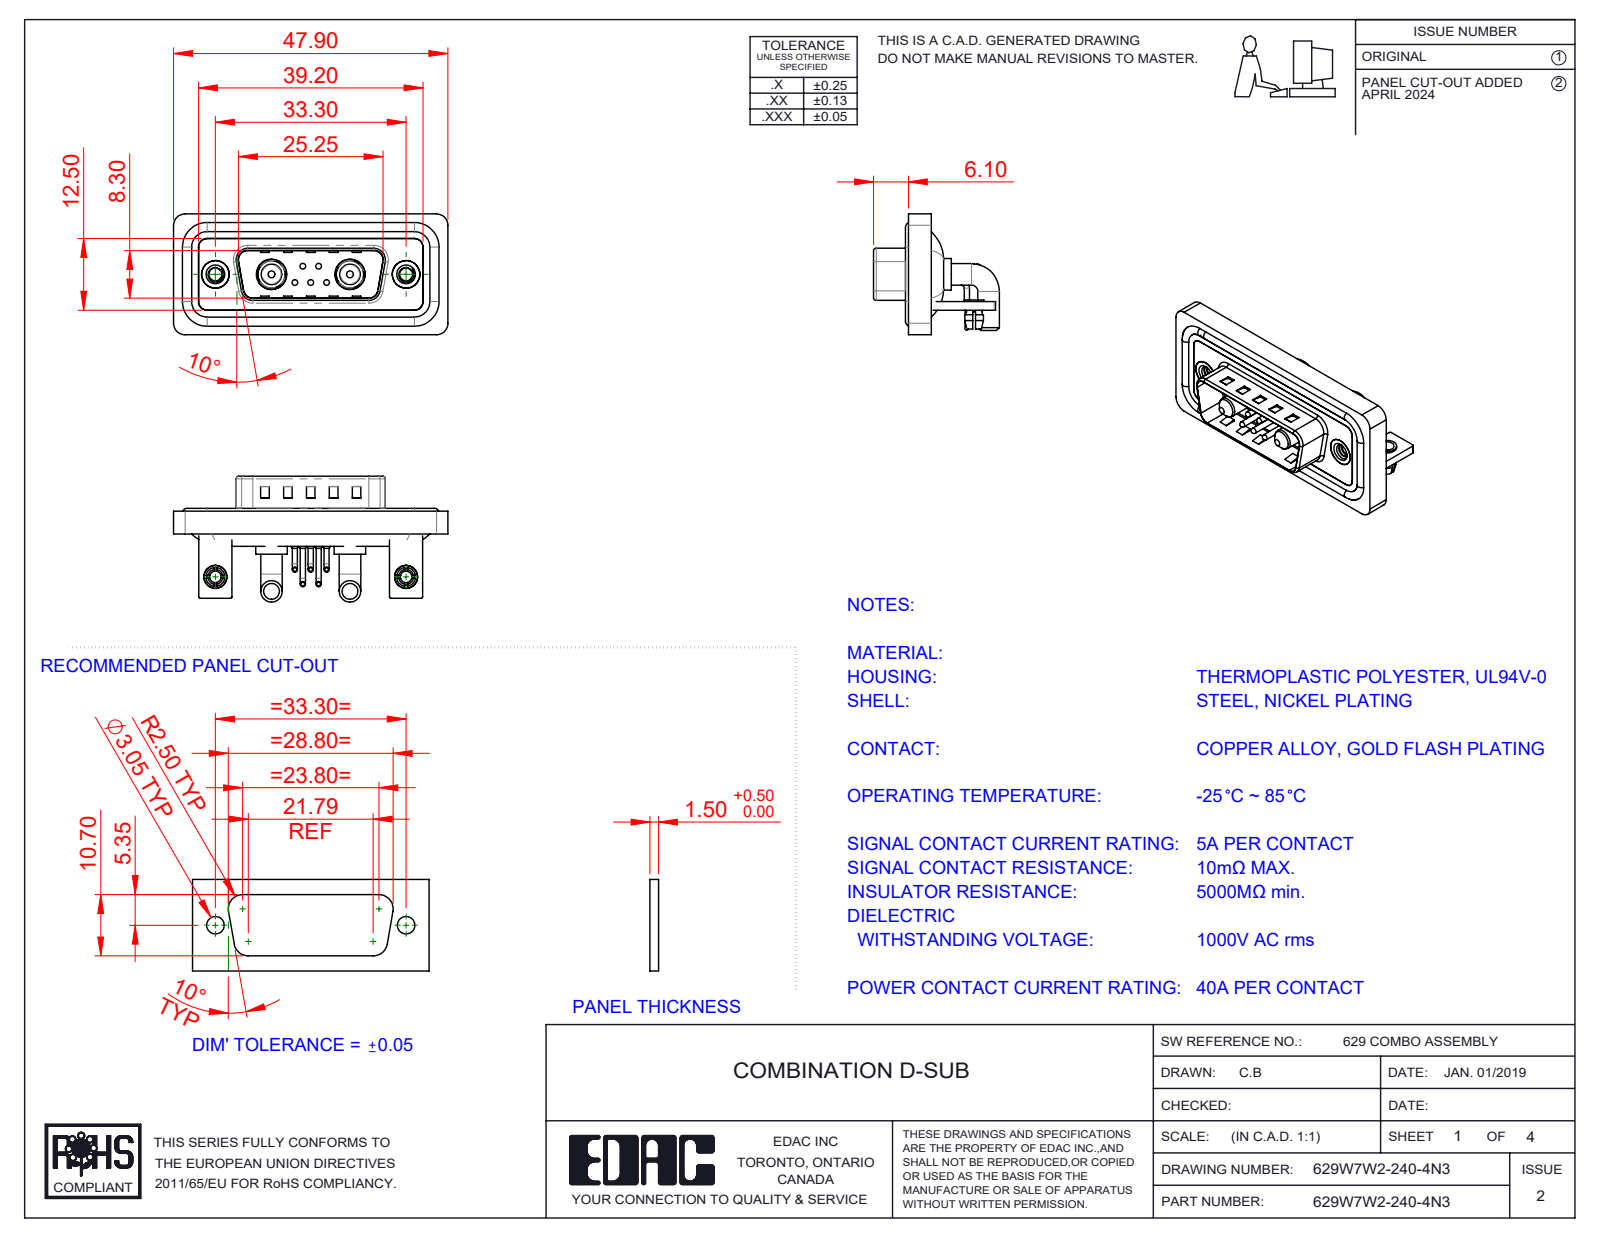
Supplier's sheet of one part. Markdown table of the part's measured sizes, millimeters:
| quantity | value |
| --- | --- |
| part name | 629Combo Board Lock; 629Combo Shell Front_15 Contacts; 629Combo Contact Row 2; 629W7W2-140-4N3 (+7 more) |
| STEP written by | SolidWorks 2023 (CONFIG_CONTROL_DESIGN) |
| units | millimeters |
| bodies | 20 solids, 1215 faces (585 planar, 456 cylindrical, 174 other) |
| overall size | 47.9 × 21.98 × 21.1 |
| volume | 6 140 mm³ |
| surface area | 10 026 mm² |
| round holes (diameter × count) | 2 × 7, 0.75 × 5, 1.6 × 5, 2.26 × 2, 2.5 × 2, 3.2 × 2, 4 × 2, 4.8 × 2, 4.85 × 2, 5 × 2, 5.3 × 2 |
| round bosses / shafts (diameter × count) | 0.9 × 10, 1.5 × 5, 1 × 5, 0.65 × 5, 3.75 × 4, 1.6 × 4, 5.5 × 2, 5.2 × 2 |
| partial cylindrical surfaces (radius × count) | 2 × 21, 1.5 × 18, 0.25 × 16, 0.5 × 9, 1.6 × 8, 1.01 × 5, 0.6 × 4, 0.65 × 4 |
| main face-to-face distances | 0.4, 0.8, 1.5, 2.9, 2.1, 1.1, 1.6, 1.2, 3.7, 4.5 |
| hole center spacings | 3.16, 2.77, 9.8, 23.5, 33.3, 4.31, 4.33, 5.03 |
